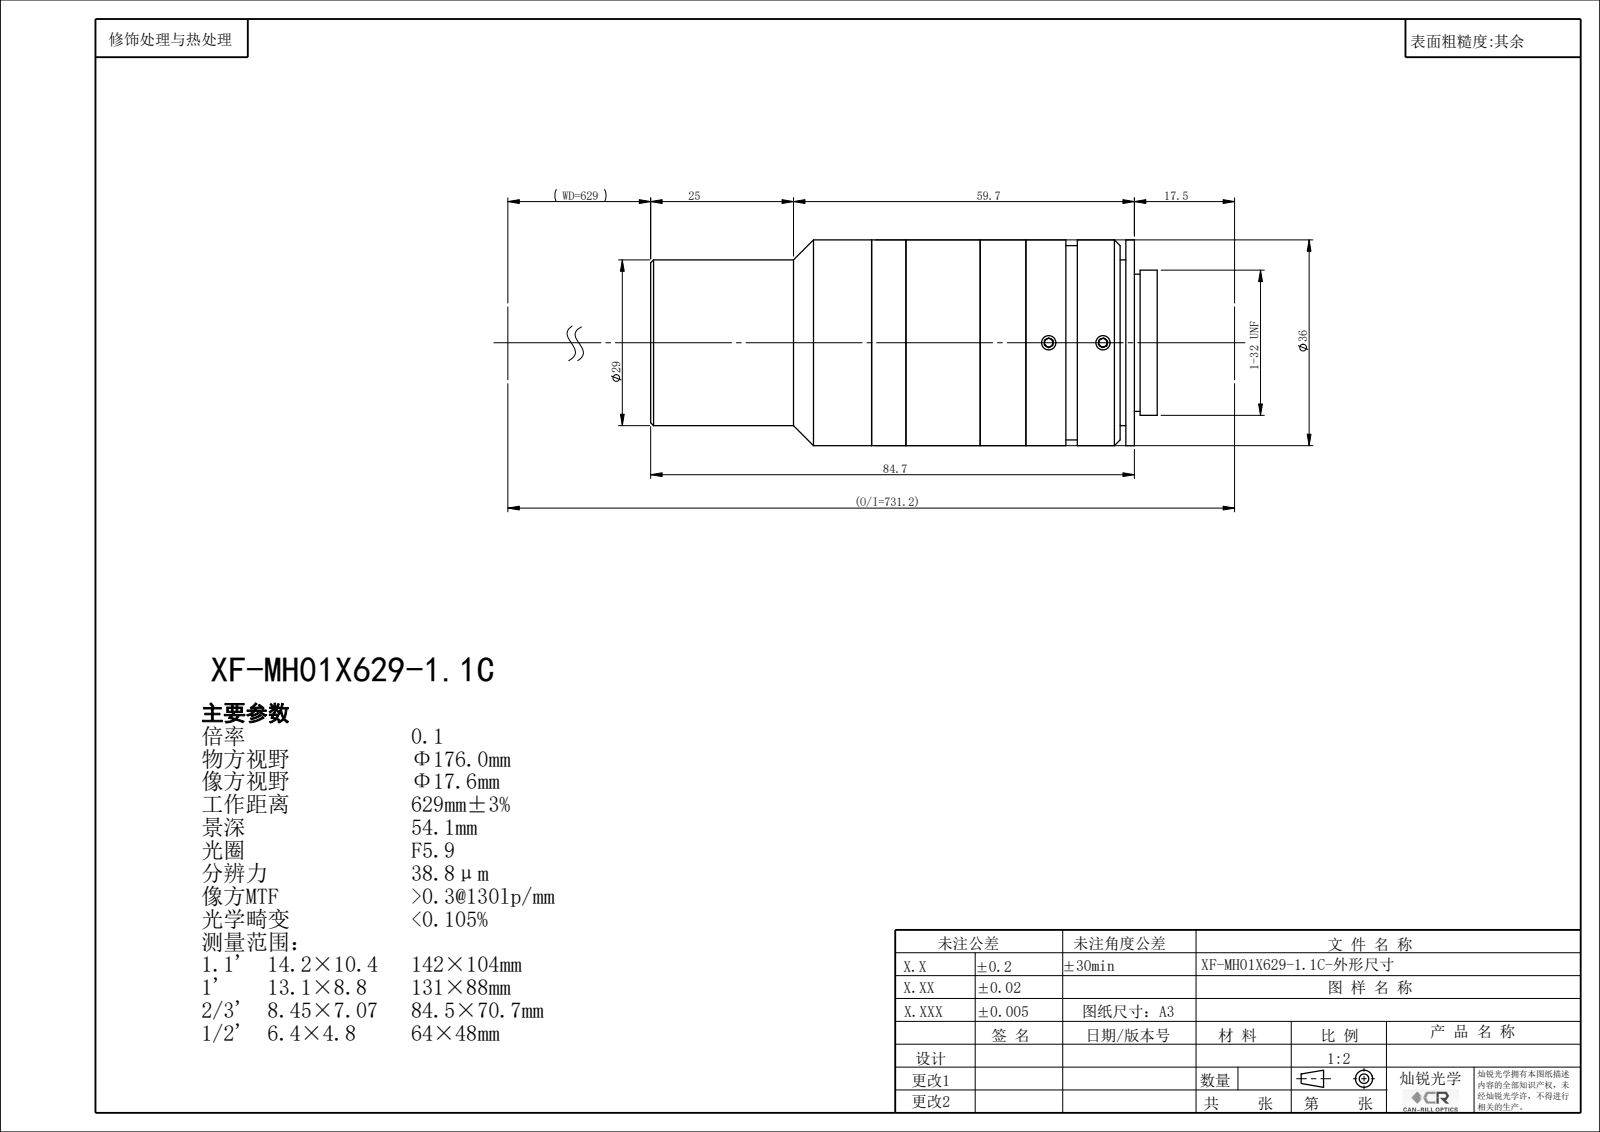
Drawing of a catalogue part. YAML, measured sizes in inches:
part_name: "XF-MH01X629-1.1C"
step_written_by: "SolidWorks 2022 (CONFIG_CONTROL_DESIGN)"
units: inches
bodies: {solids: 0, faces: 136, planar: 66, cylindrical: 48, other: 22}
overall_size: [3.491, 1.417, 1.417]
round_holes:
  - {diameter: 0.098, count: 6}
  - {diameter: 0.787, count: 1}
  - {diameter: 0.882, count: 1}
  - {diameter: 0.945, count: 1}
  - {diameter: 0.98, count: 1}
  - {diameter: 1.024, count: 1}
  - {diameter: 1.039, count: 1}
round_bosses_or_shafts:
  - {diameter: 1.417, count: 1}
  - {diameter: 1.339, count: 1}
  - {diameter: 1.142, count: 1}
  - {diameter: 1, count: 1}
face_to_face_distances: [0.748, 0.059, 0.689, 0.315, 1.004, 1.063, 0.236, 0.551, 0.452, 0.511]
hole_center_spacings: [0.374]
